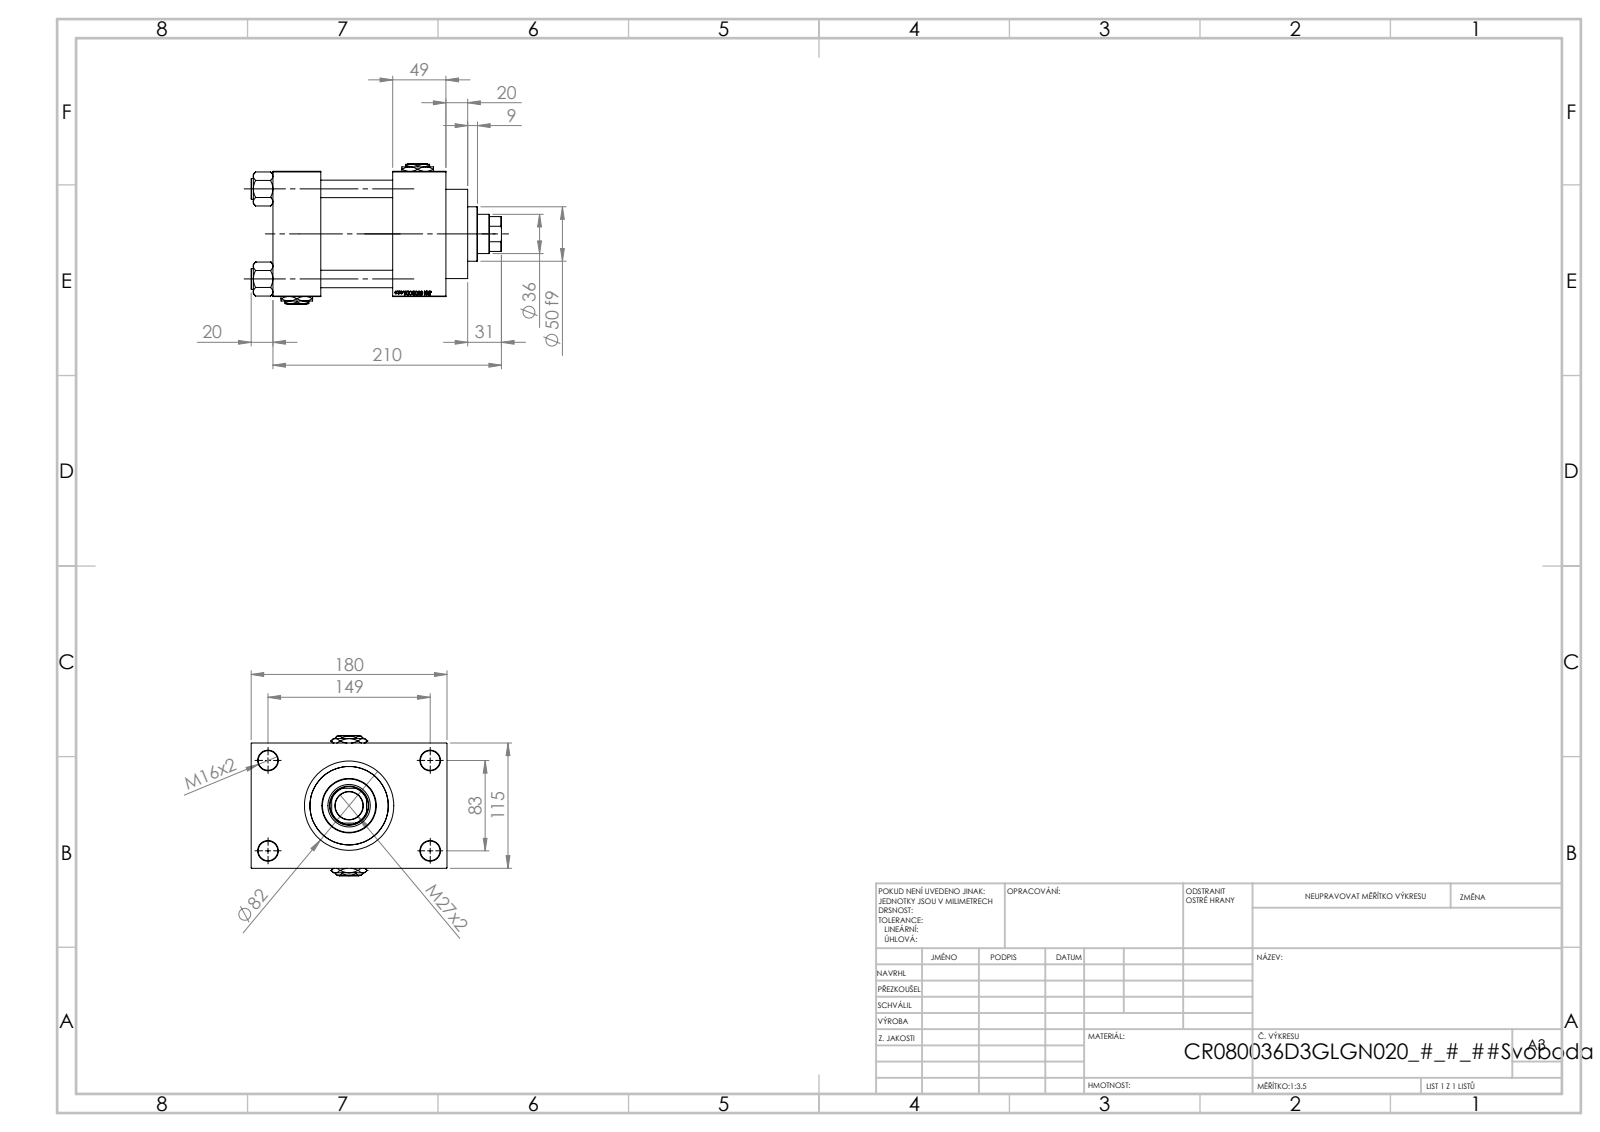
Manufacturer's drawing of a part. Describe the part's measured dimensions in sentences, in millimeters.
The part is named "V215_VC_A; V215CR_D_TYCINKA; Zatka_pro_OIL_PORT; NUT_M5_D (+2 more)". Its 3-D file was written by "SolidWorks 2019 (CONFIG_CONTROL_DESIGN)". It is 13 solids with 1236 faces: 589 planar, 89 cylindrical and 558 other. Overall it measures 230 by 180 by 129 millimeters. Its volume is 2 005 000 cubic millimeters and its surface area 297 927 square millimeters. Round holes: 4 of diameter 16, 4 of diameter 18, 2 of diameter 7, 2 of diameter 26.44, 2 of diameter 35, 1 of diameter 25.5, 1 of diameter 36, 1 of diameter 39, 1 of diameter 61, 1 of diameter 72, 1 of diameter 80. Round bosses or shafts: 4 of diameter 19, 1 of diameter 86, 1 of diameter 82, 1 of diameter 50. Partial cylindrical surfaces (rounded edges, fillets, slot ends): 1 of radius 17.5. The main face-to-face distances are 115, 66, 110, 49, 44, 159, 147.5, 32.5, 20, 69. The hole center spacings are 33.15, 58.48, 82.7, 85.28, 89.24, 115.85, 142.43, 83.
